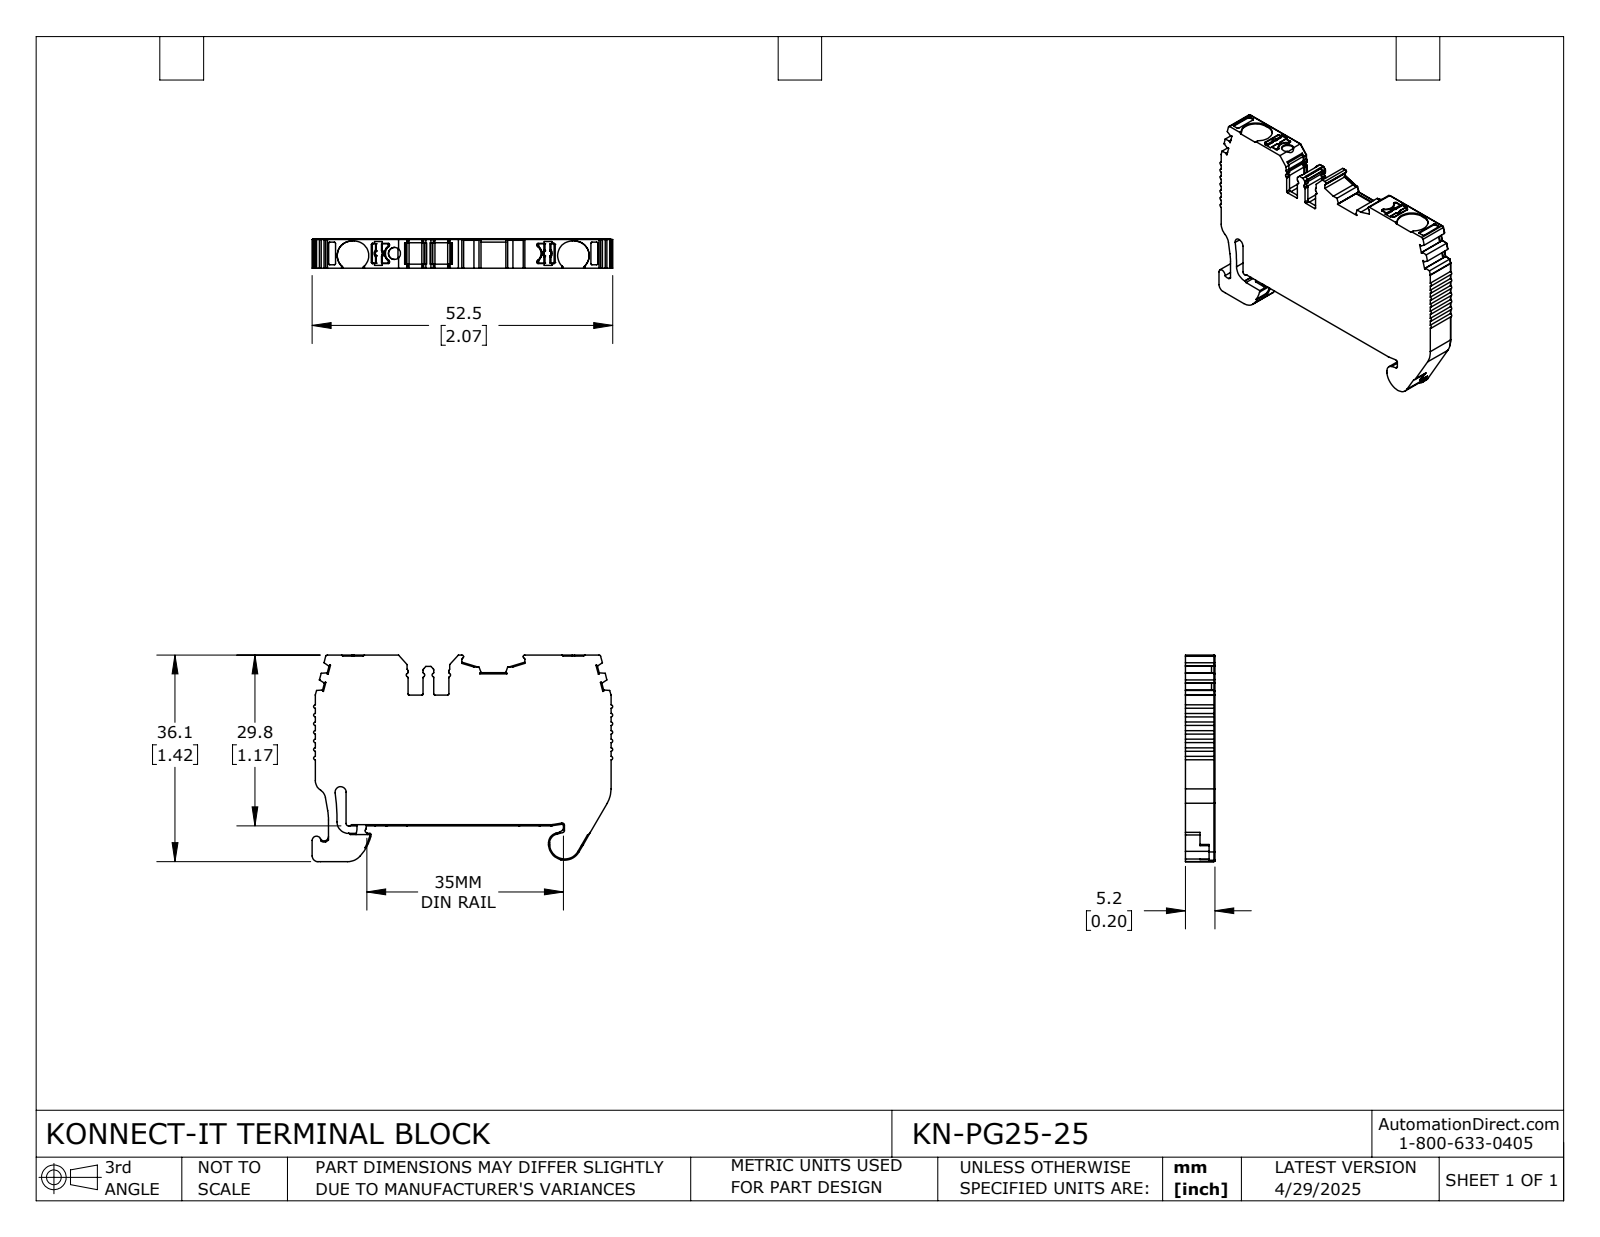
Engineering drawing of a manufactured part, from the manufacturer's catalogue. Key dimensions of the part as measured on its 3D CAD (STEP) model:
Part name (STEP PRODUCT): KN-PG25-25
STEP written by: SolidWorks 2024 (CONFIG_CONTROL_DESIGN)
Units: millimetres
Bodies: 1 solid, 634 faces (336 planar, 261 cylindrical, 37 other)
Overall size (bounding box): 52.48 × 36.07 × 5.15
Volume: 7 631 mm³ · Surface area: 4 324 mm²
Round holes (diameter × count): ⌀2.1 ×1
Partial cylindrical surfaces — rounded edges, fillets, slot ends (radius × count): R0.2 ×53, R0.3 ×42, R0.4 ×18, R0.1 ×17, R0.5 ×16, R0.15 ×8, R1 ×6, R2.55 ×4
Main face-to-face distances: 5.15, 29.61, 29.41, 29.81, 51.63, 4.5, 5, 5.37, 46.26, 6.26
